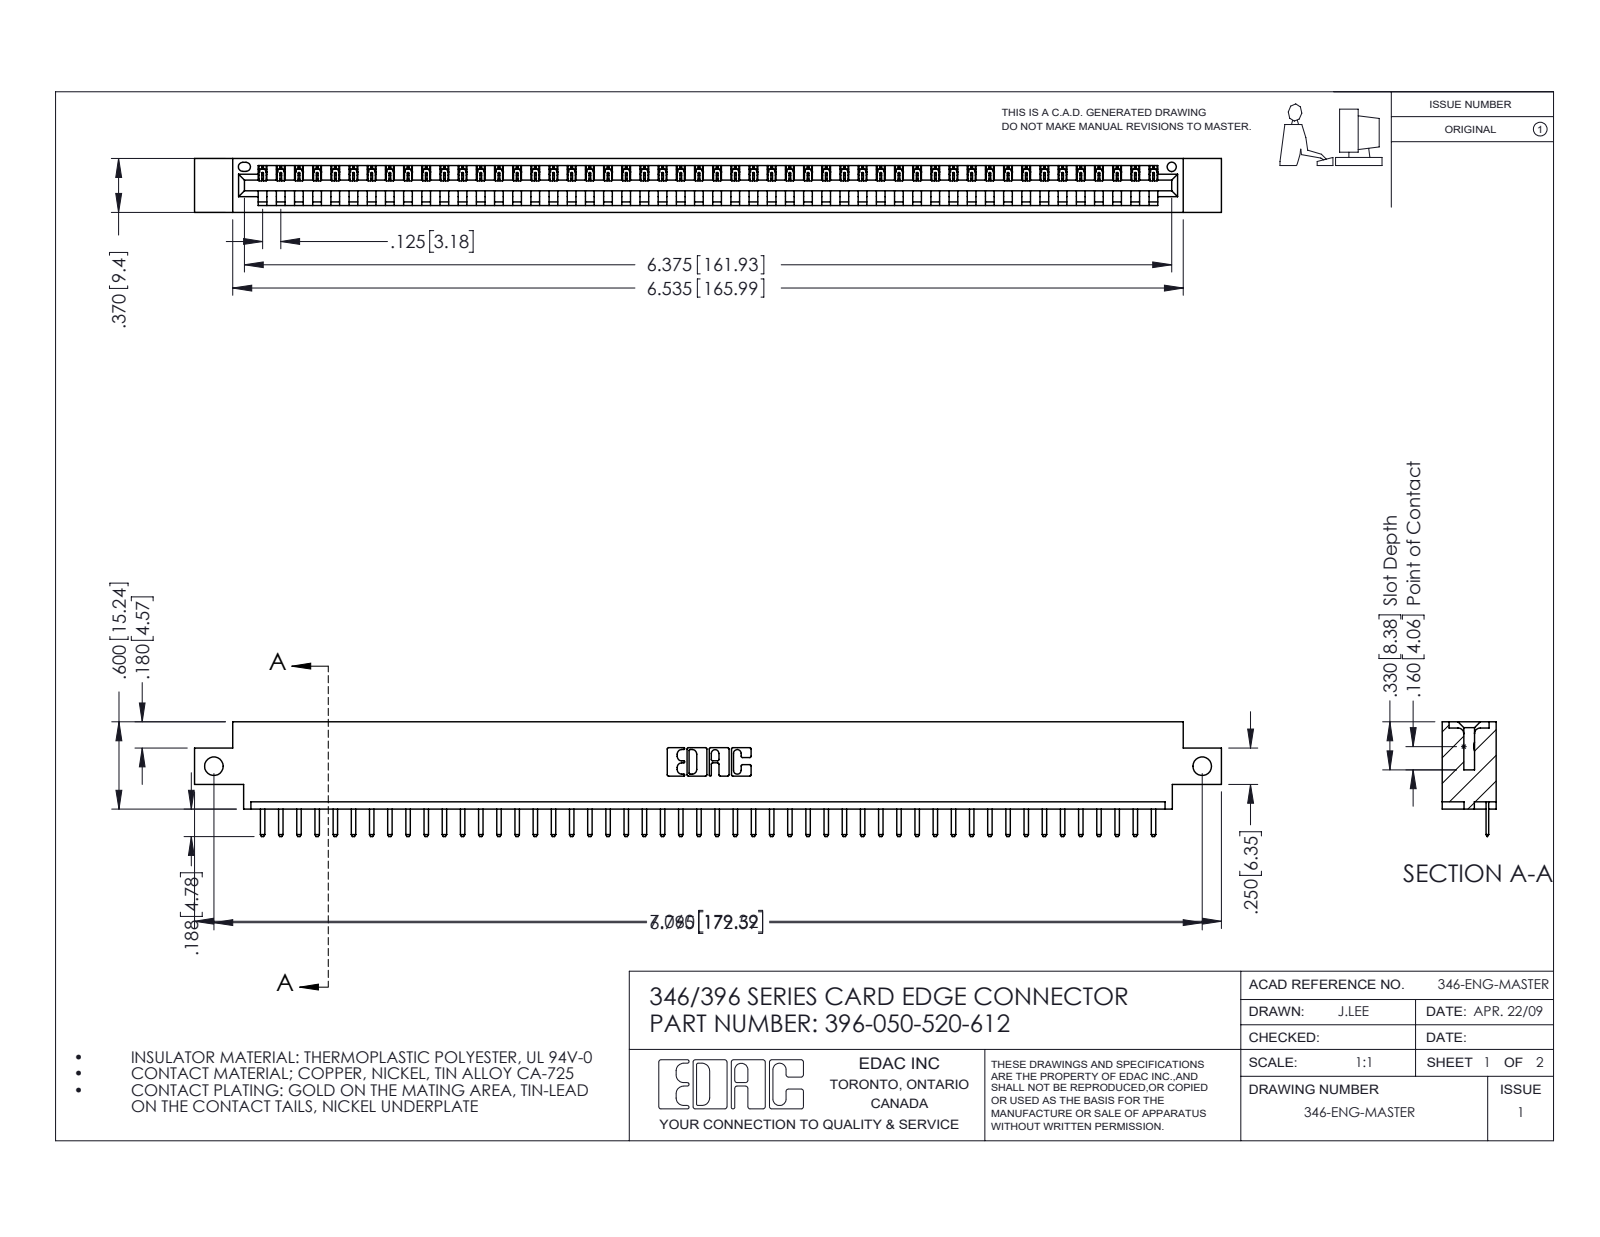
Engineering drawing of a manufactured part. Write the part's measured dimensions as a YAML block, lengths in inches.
part_name: "345-292-001_345-293-120; 346 Part_0.170 Offset - Side Mount; 396-050-520-612"
step_written_by: "SolidWorks 2016 (CONFIG_CONTROL_DESIGN)"
units: inches
bodies: {solids: 51, faces: 3226, planar: 2180, cylindrical: 1046, other: 0}
overall_size: [7.06, 0.788, 0.37]
volume: 1.027
surface_area: 32.03
round_holes:
  - {diameter: 0.128, count: 2}
  - {diameter: 0.064, count: 1}
partial_cylinders:
  - {radius: 0.01, count: 102}
  - {radius: 0.006, count: 100}
  - {radius: 0.01, count: 22}
  - {radius: 0.007, count: 6}
  - {radius: 0.031, count: 6}
  - {radius: 0.026, count: 3}
  - {radius: 0.031, count: 2}
  - {radius: 0.04, count: 2}
face_to_face_distances: [0.048, 0.322, 0.37, 0.25, 0.148, 0.222, 0.1, 0.174, 0.072, 0.298]
hole_center_spacings: [6.795]
